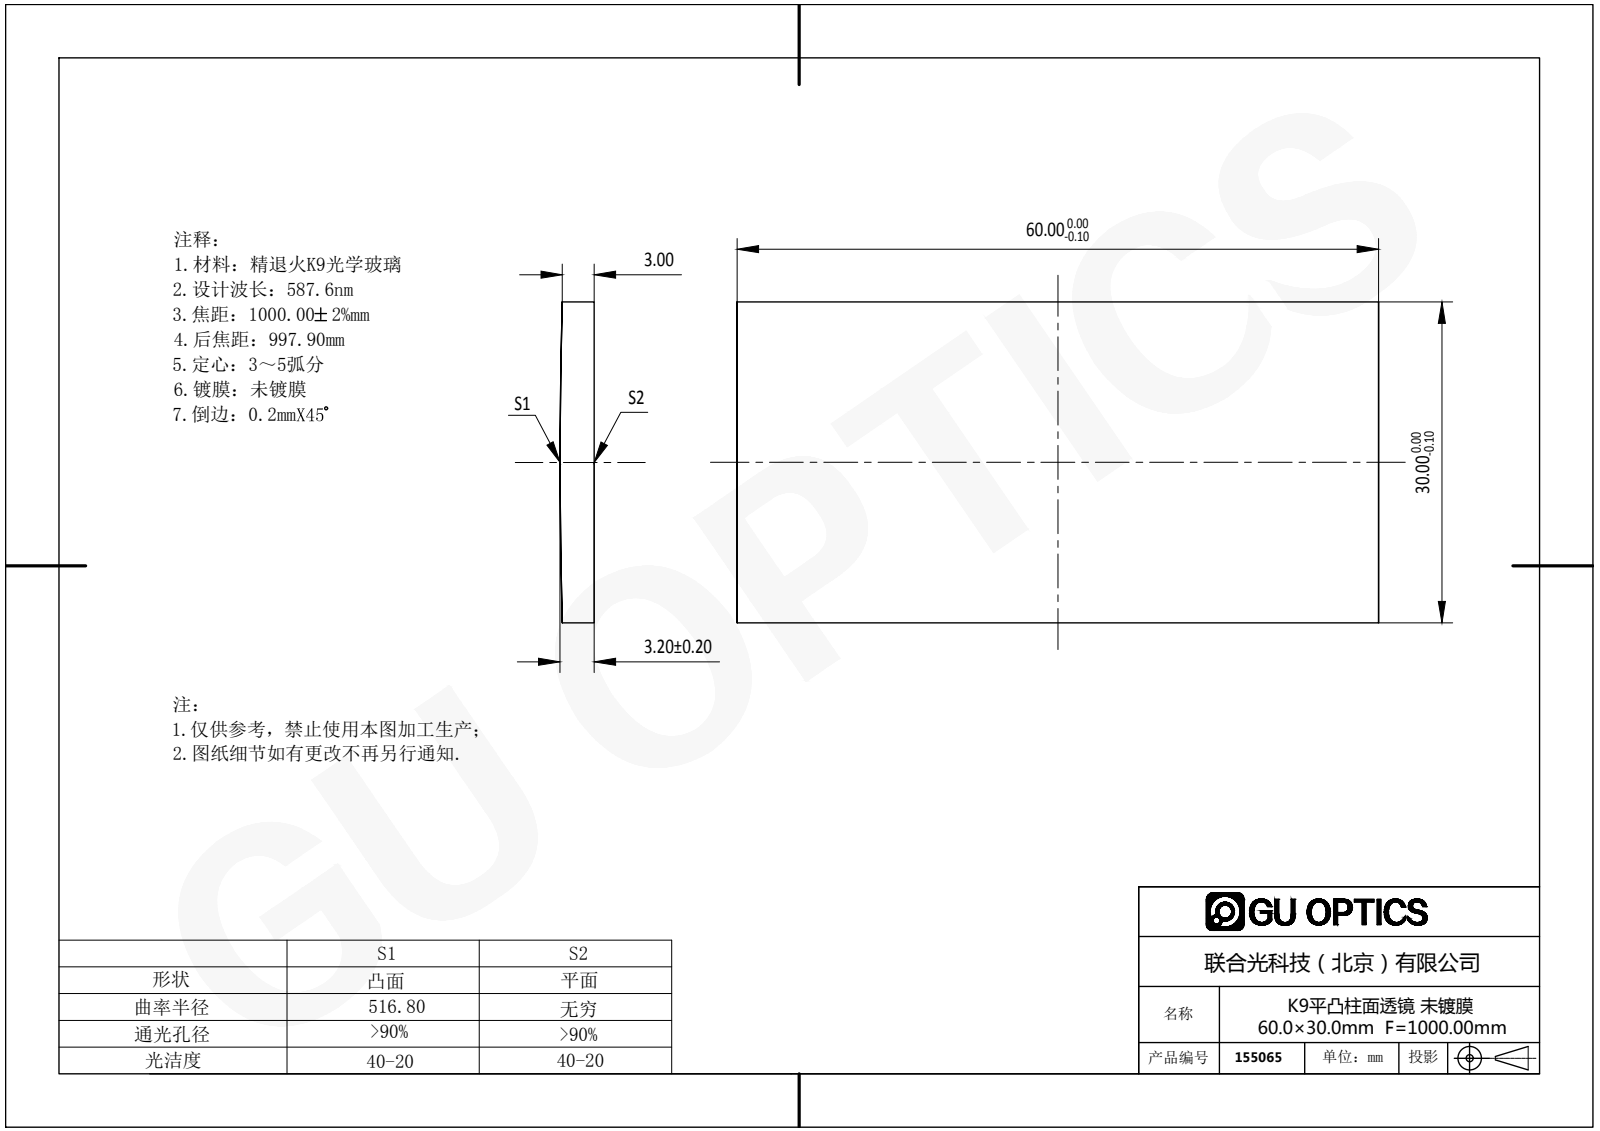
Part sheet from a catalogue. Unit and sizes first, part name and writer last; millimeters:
Units: millimetres
Overall size (bounding box): 60 × 30 × 3.2
Partial cylindrical surfaces — rounded edges, fillets, slot ends (radius × count): R516.8 ×1
Main face-to-face distances: 30, 60
Volume: 5 629 mm³ · Surface area: 4 146 mm²
Bodies: 1 solid, 6 faces (5 planar, 1 cylindrical, 0 other)
Part name (STEP PRODUCT): 155065
STEP written by: SolidWorks 2016 (AUTOMOTIVE_DESIGN)
